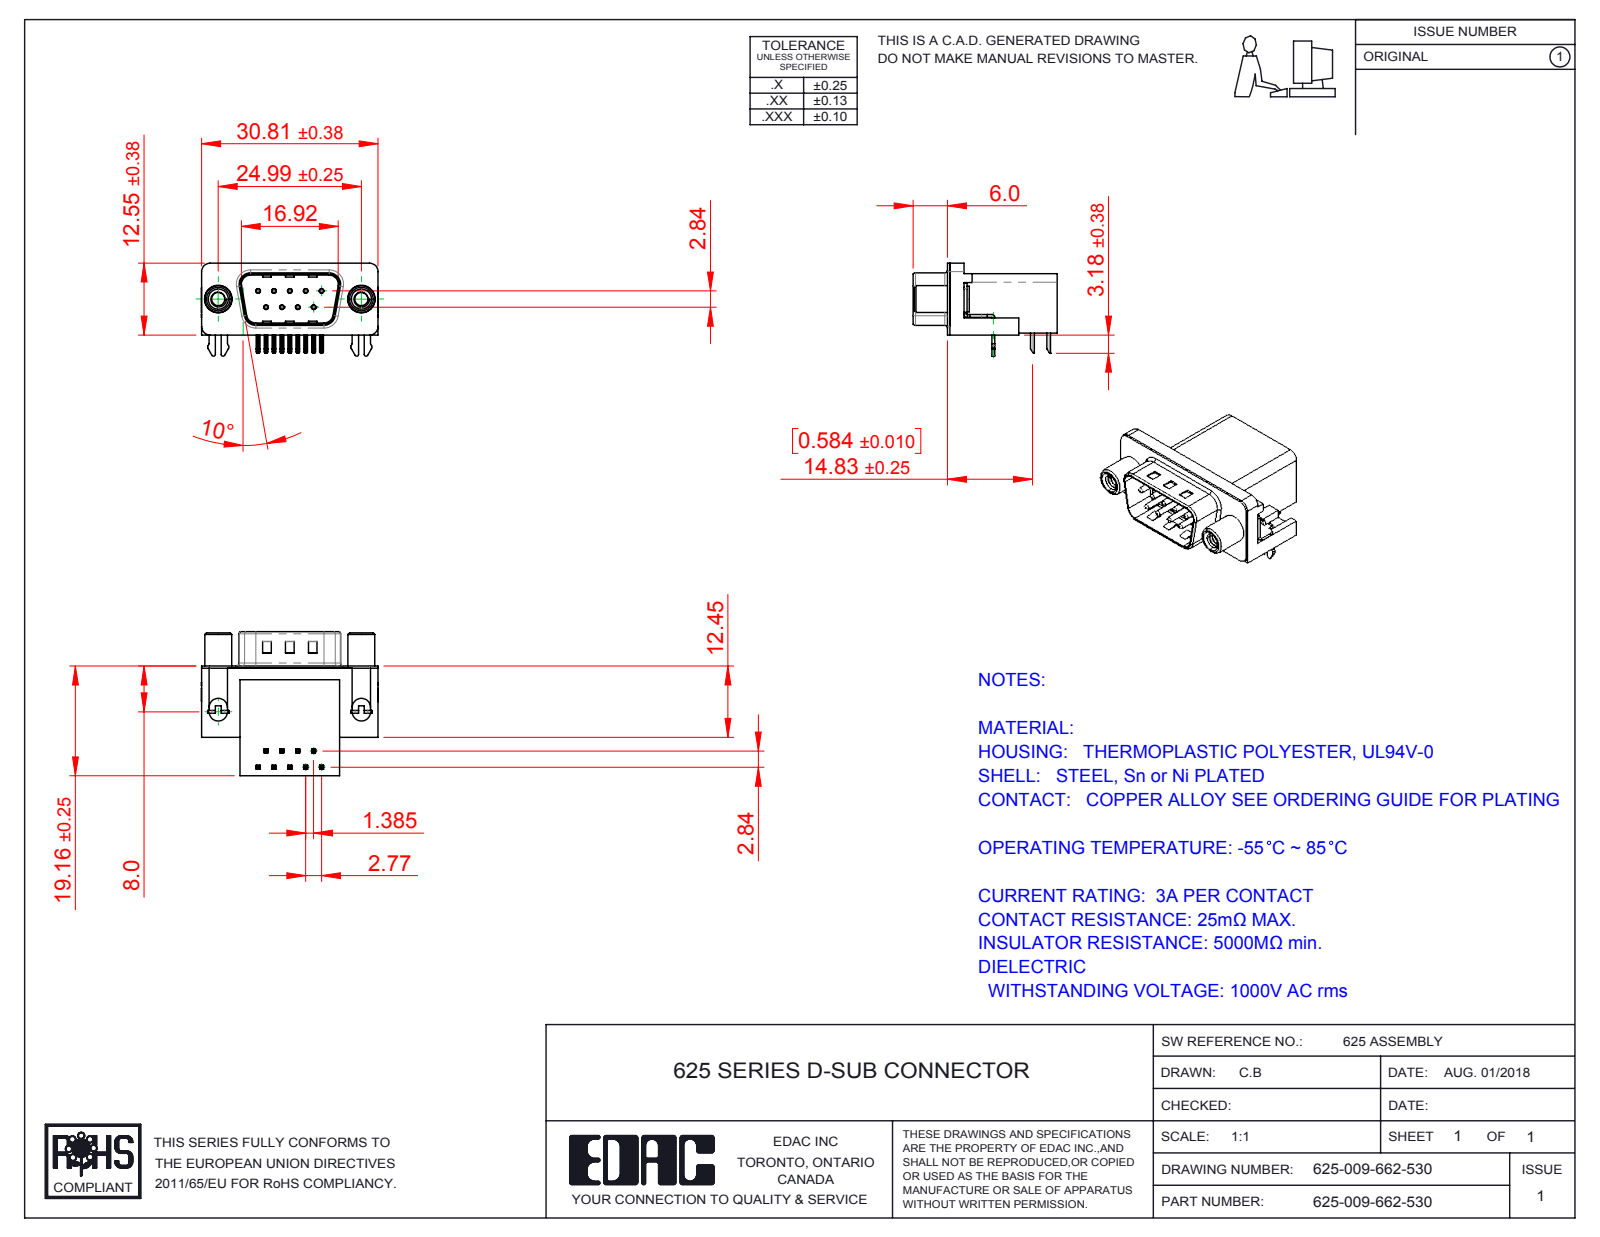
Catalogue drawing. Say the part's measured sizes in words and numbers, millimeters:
The part is named "625 2 Prong Board Lock; 625 Round Threaded Standoff; 625 Shell_9 Socket; 625-009-662-530 (+3 more)". Its 3-D file was written by "SolidWorks 2016 (CONFIG_CONTROL_DESIGN)". It is 15 solids with 1027 faces: 597 planar, 333 cylindrical and 97 other. Overall it measures 30.89 by 25.16 by 16.25 millimeters. Its volume is 4 565 cubic millimeters and its surface area 5 156 square millimeters. Round holes: 9 of diameter 0.35, 9 of diameter 0.8, 2 of diameter 2.3, 2 of diameter 3.1, 2 of diameter 4, 2 of diameter 4.8, 2 of diameter 5. Round bosses or shafts: 9 of diameter 0.75, 2 of diameter 4.9, 2 of diameter 4.7, 2 of diameter 4.5, 2 of diameter 3.85. Partial cylindrical surfaces (rounded edges, fillets, slot ends): 36 of radius 0.25, 18 of radius 0.12, 16 of radius 1, 14 of radius 0.5, 8 of radius 1.5, 8 of radius 1.6, 4 of radius 0.32, 4 of radius 0.9. The main face-to-face distances are 0.4, 10.34, 18.76, 19.16, 16.26, 2.5, 2.9, 0.35, 10.69, 6.7. The hole center spacings are 3.16, 2.77, 5.54, 5.03, 5.04, 8.31, 7.48, 7.49.
